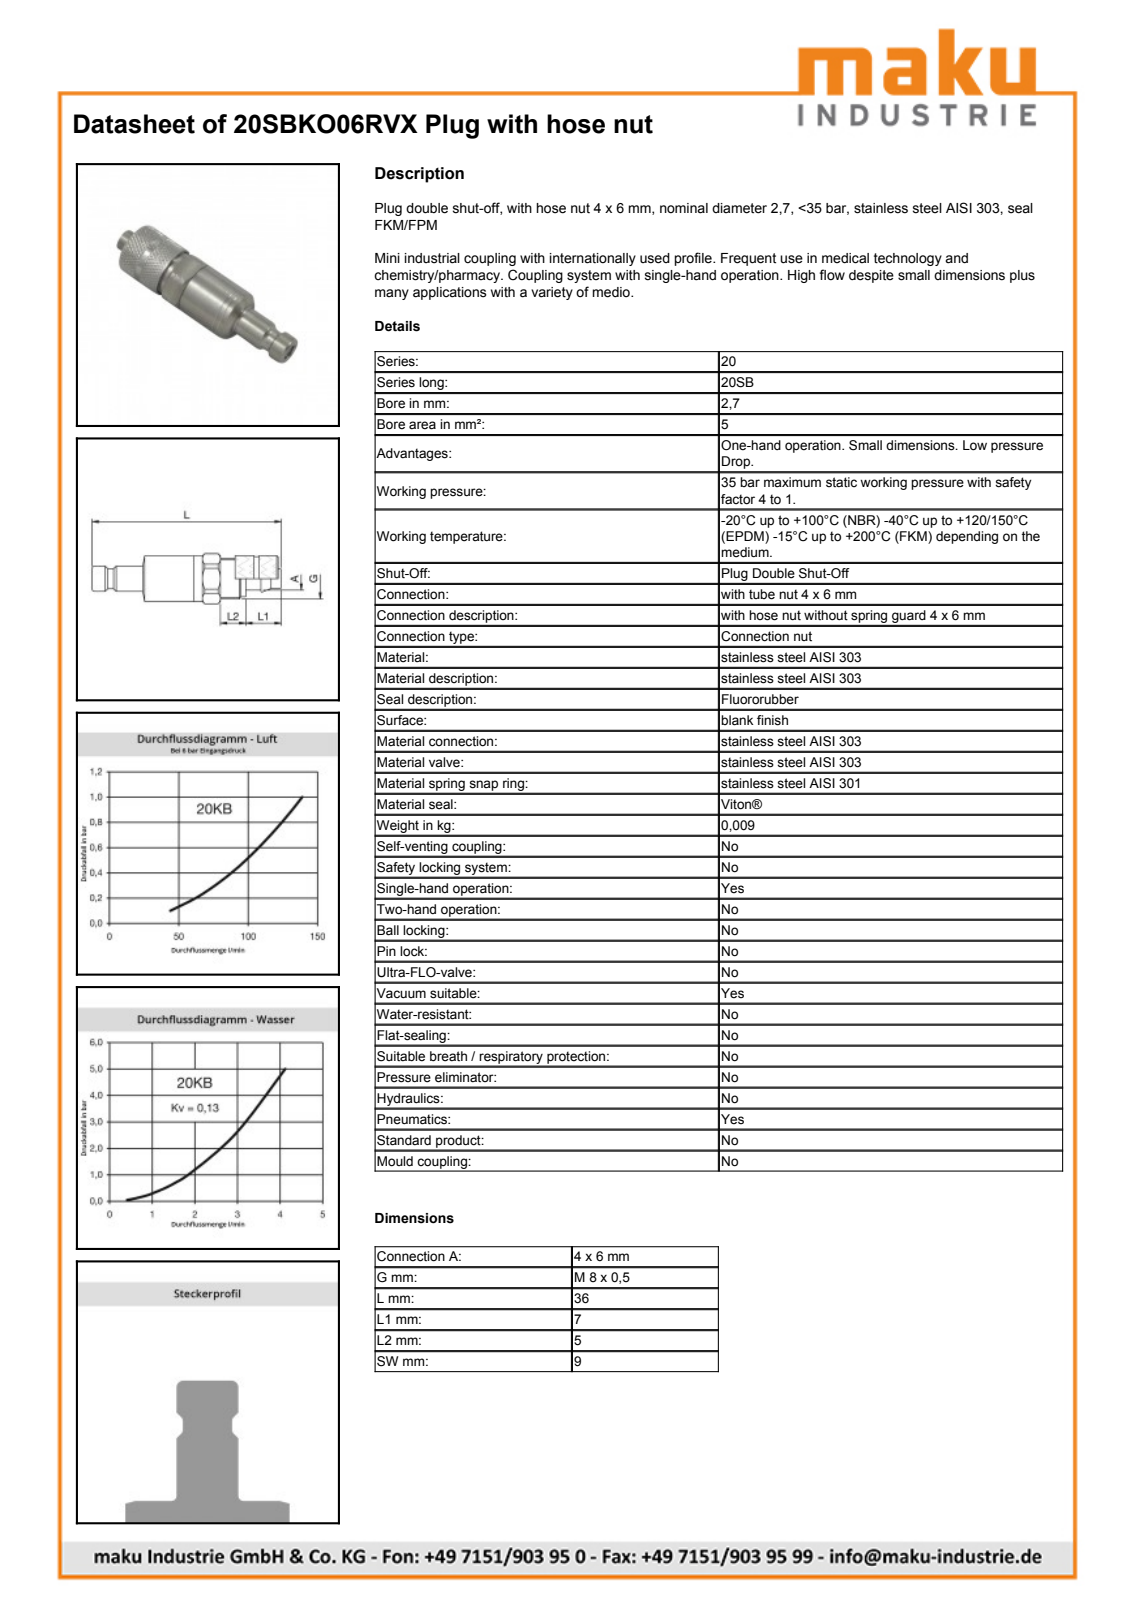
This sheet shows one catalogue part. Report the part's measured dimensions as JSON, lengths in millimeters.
{"part_name": "D113237", "step_written_by": "Autodesk Inventor 2013 (AUTOMOTIVE_DESIGN)", "units": "millimeters", "bodies": {"solids": 1, "faces": 68, "planar": 17, "cylindrical": 21, "other": 30}, "overall_size": [35.55, 9.9, 9.1], "volume_mm3": 1643, "surface_area_mm2": 1229, "round_holes": [[7.46, 1], [8, 1], [8.1, 1]], "round_bosses_or_shafts": [[9.1, 1], [9, 1], [8.7, 1], [7.3, 1], [7.04, 1], [5, 1], [3.95, 1], [3.85, 1]], "partial_cylinders_radius": [[4.95, 1]], "face_to_face_distances": [9, 10, 4.75, 13.05, 20, 1, 23.05, 13.55, 3.55, 9.5]}
